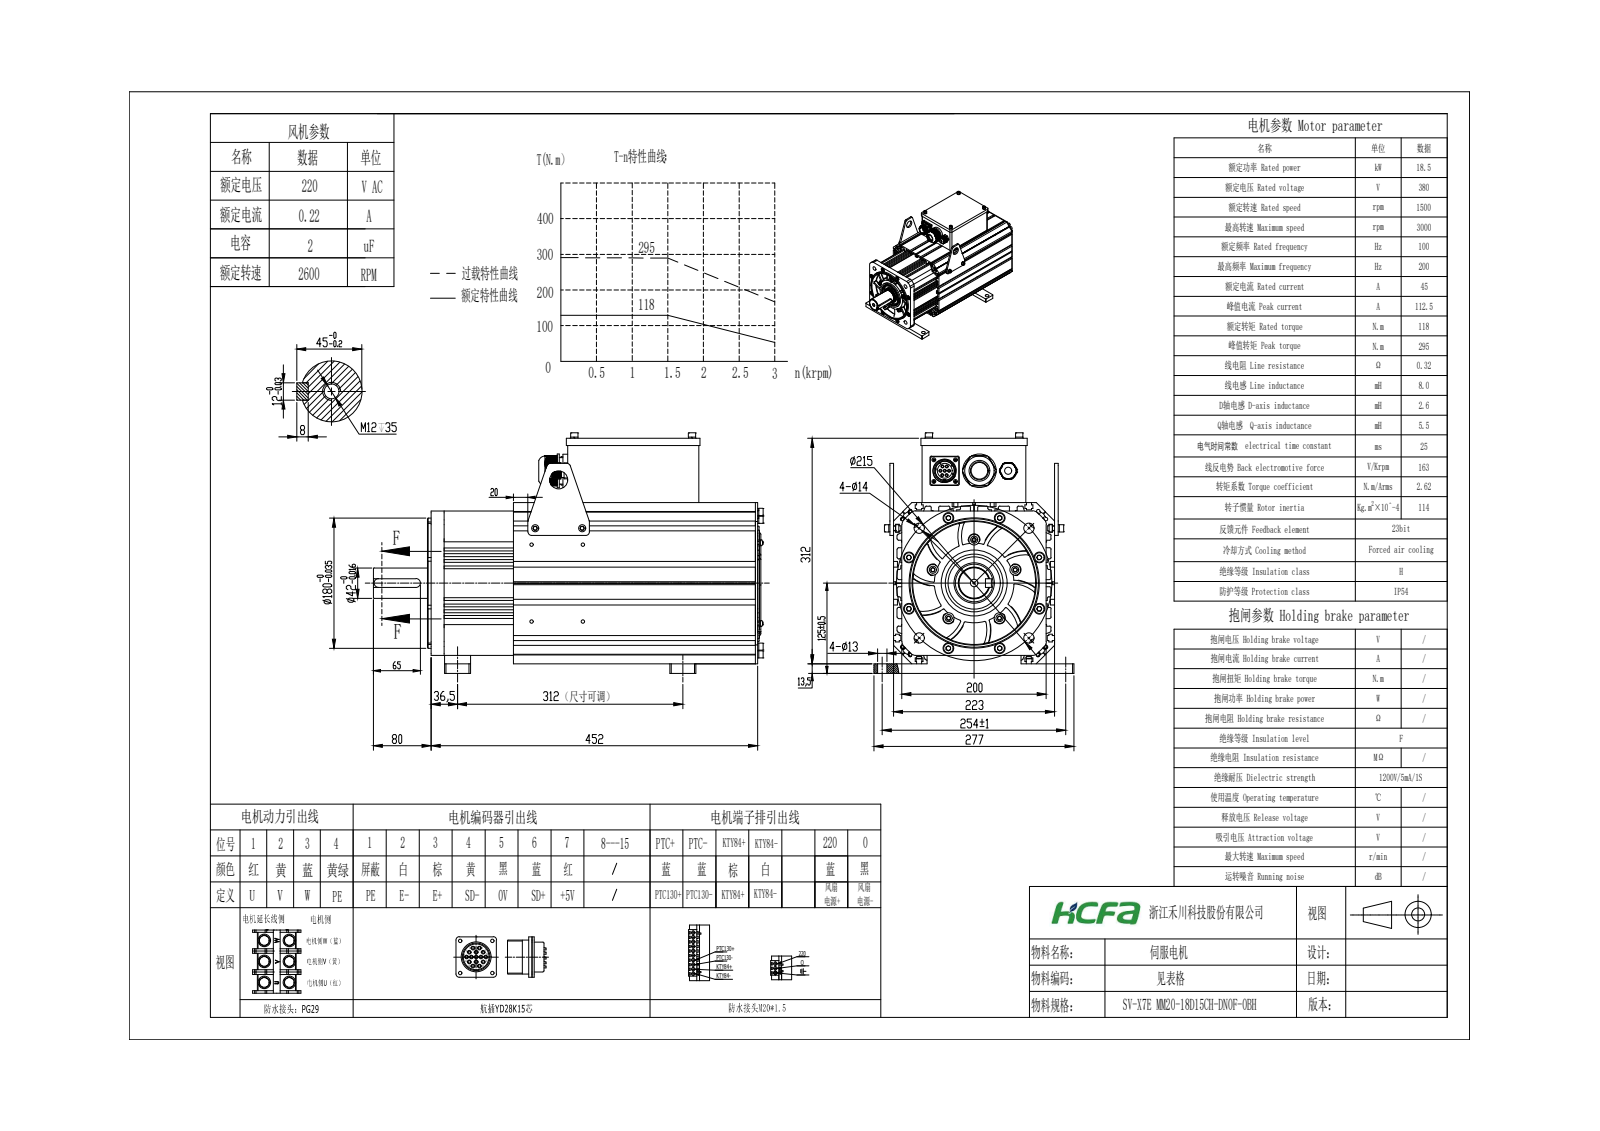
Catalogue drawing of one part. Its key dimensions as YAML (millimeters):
part_name: "18.5KW"
step_written_by: "SolidWorks 2021 (CONFIG_CONTROL_DESIGN)"
units: millimeters
bodies: {solids: 111, faces: 4173, planar: 2310, cylindrical: 1117, other: 746}
overall_size: [539.6, 333.1, 277]
volume: 6337000
surface_area: 2329000
round_holes:
  - {diameter: 2.5, count: 19}
  - {diameter: 6.5, count: 19}
  - {diameter: 6.68, count: 19}
  - {diameter: 4.2, count: 16}
  - {diameter: 9, count: 14}
  - {diameter: 15, count: 10}
  - {diameter: 6.8, count: 8}
  - {diameter: 4.5, count: 6}
  - {diameter: 14, count: 5}
  - {diameter: 3.2, count: 4}
  - {diameter: 3.4, count: 4}
  - {diameter: 4.4, count: 4}
round_bosses_or_shafts:
  - {diameter: 2, count: 24}
  - {diameter: 10, count: 19}
  - {diameter: 9.88, count: 19}
  - {diameter: 6, count: 19}
  - {diameter: 3, count: 19}
  - {diameter: 3.5, count: 15}
  - {diameter: 8, count: 12}
  - {diameter: 13, count: 8}
partial_cylinders:
  - {radius: 2, count: 89}
  - {radius: 5, count: 16}
  - {radius: 1.5, count: 8}
  - {radius: 2.41, count: 8}
  - {radius: 2.5, count: 8}
  - {radius: 3, count: 8}
  - {radius: 10, count: 8}
  - {radius: 7.5, count: 5}
face_to_face_distances: [223, 11.5, 6.5, 2.5, 211.5, 5, 206.5, 218, 13, 210]
hole_center_spacings: [132, 25.45, 39.3, 42.89, 50.36, 52.92, 63.06, 97]
